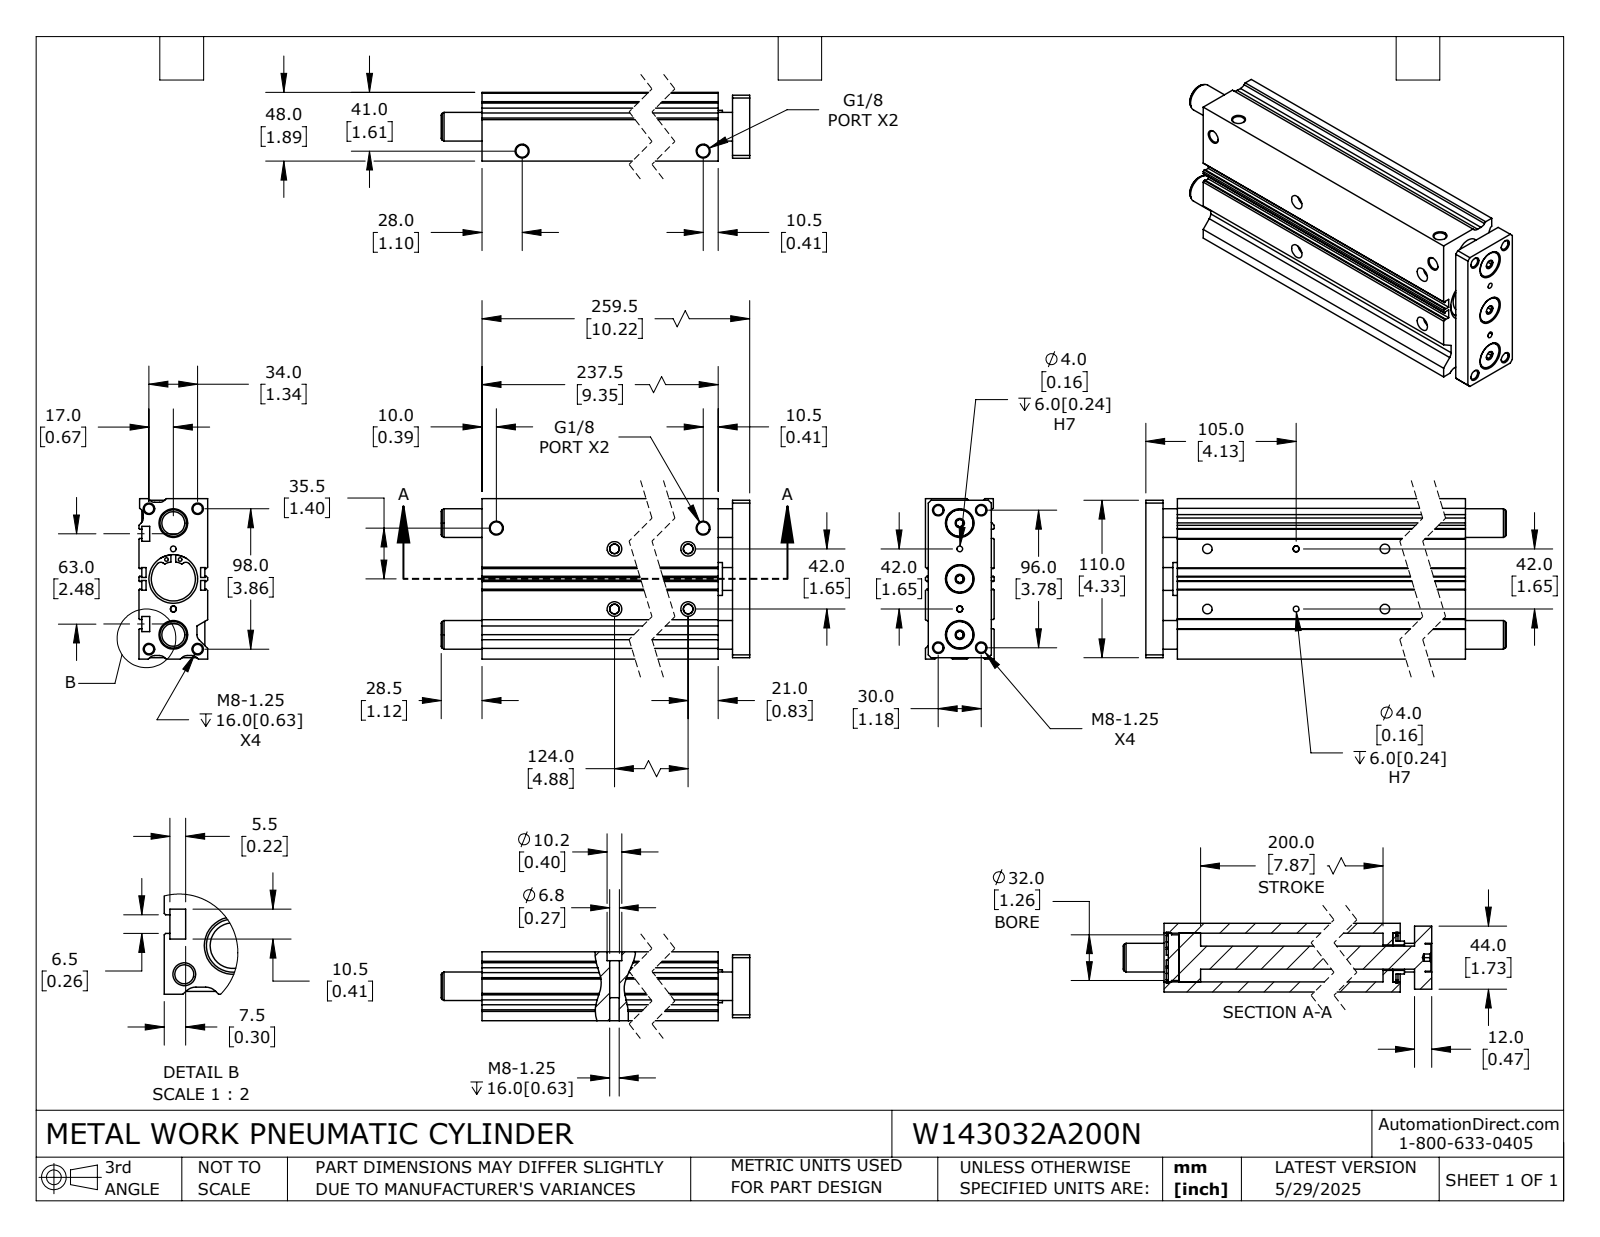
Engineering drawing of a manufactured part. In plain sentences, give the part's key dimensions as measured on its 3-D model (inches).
The part is named "W143032A200N_ROD; W143032A200N; W143032A200N_BODY". Its 3-D file was written by "SolidWorks 2024 (CONFIG_CONTROL_DESIGN)". It is 6 solids with 394 faces: 195 planar, 149 cylindrical and 50 other. Overall it measures 11.339 by 4.409 by 1.89 inches. Its volume is 66.31 cubic inches and its surface area 375.4 square inches. Round holes: 12 of diameter 0.262, 4 of diameter 0.098, 4 of diameter 0.157, 4 of diameter 0.268, 4 of diameter 0.337, 4 of diameter 0.402, 3 of diameter 0.197, 3 of diameter 0.787, 1 of diameter 0.697, 1 of diameter 1.211. Round bosses or shafts: 3 of diameter 0.748, 2 of diameter 1.406, 1 of diameter 1.339, 1 of diameter 1.26, 1 of diameter 0.906, 1 of diameter 0.63. Partial cylindrical surfaces (rounded edges, fillets, slot ends): 9 of radius 0.197, 4 of radius 0.079, 4 of radius 0.118, 2 of radius 0.507. The main face-to-face distances are 1.89, 0.295, 0.098, 0.118, 1.693, 0.197, 1.594, 0.079, 4.409, 1.398. The hole center spacings are 0.088, 0.348, 0.566, 0.689, 0.776, 1.019, 1.216, 1.261.
